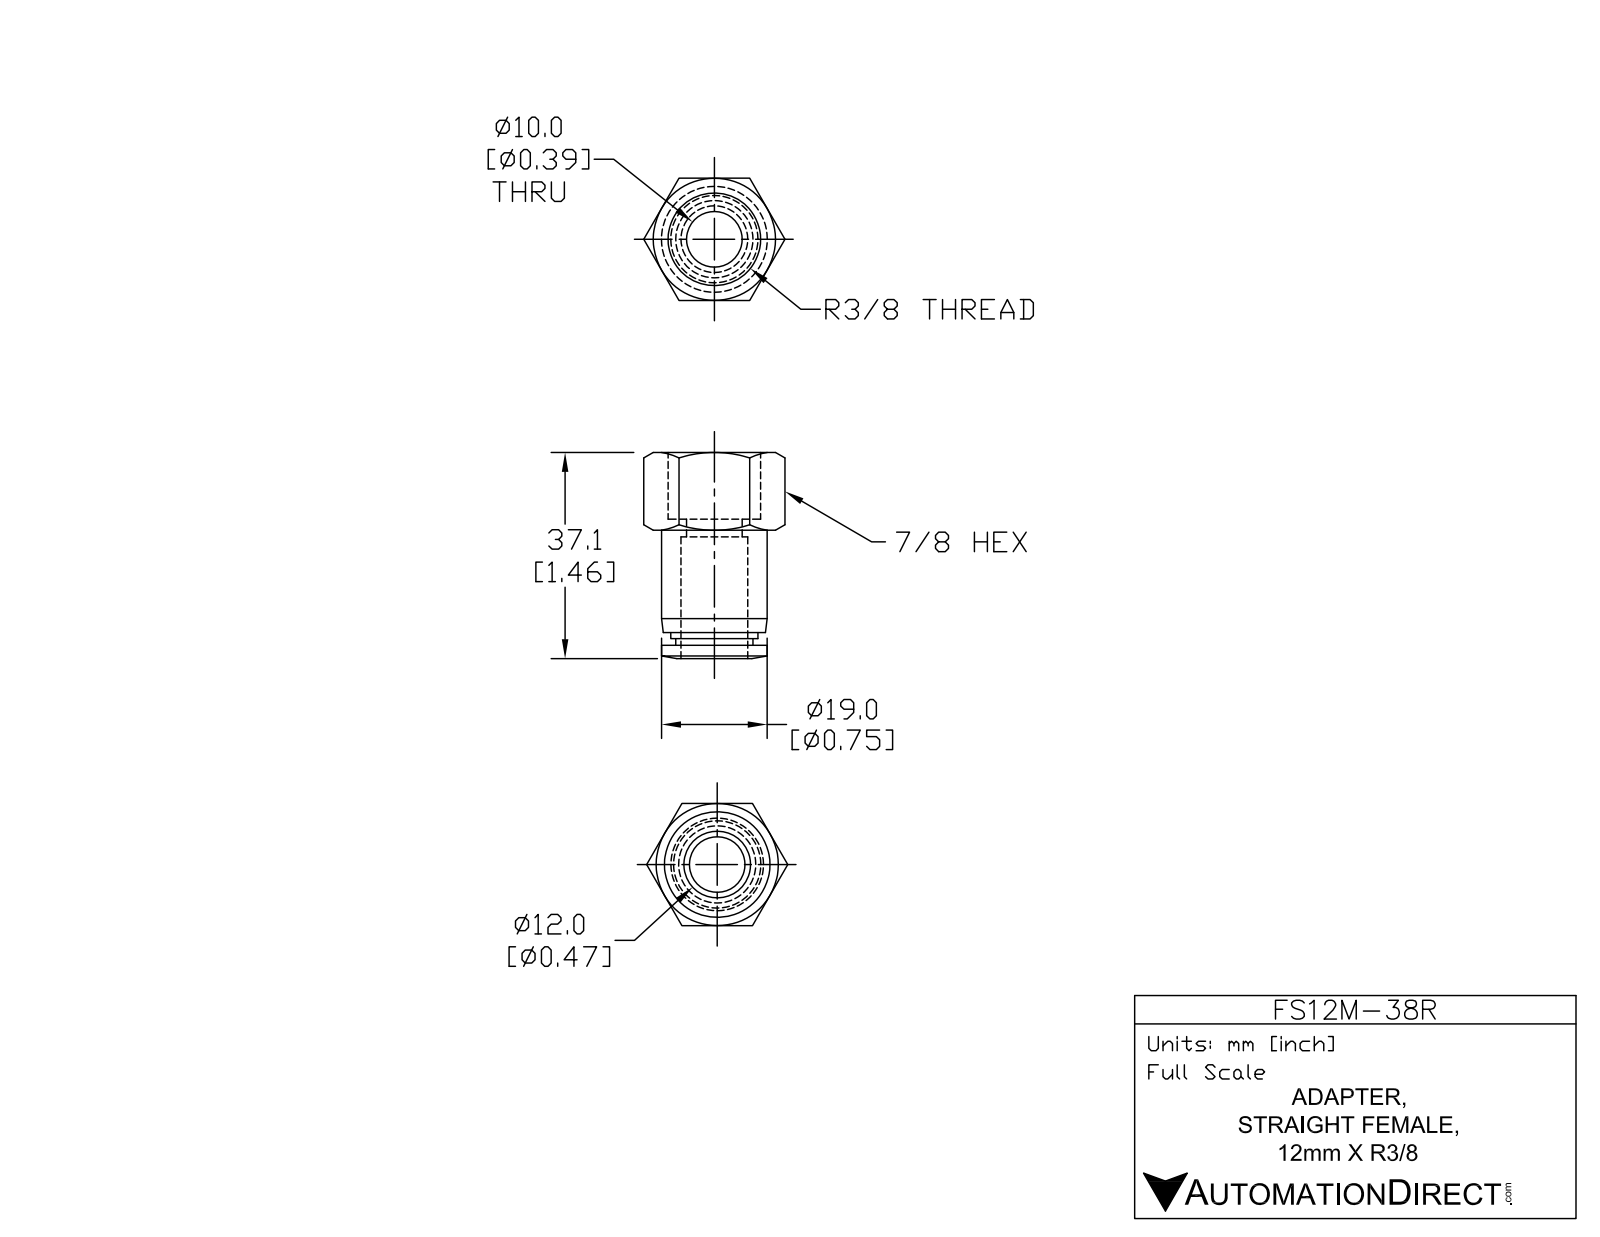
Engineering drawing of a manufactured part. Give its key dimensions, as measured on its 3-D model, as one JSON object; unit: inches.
{"part_name": "FS12M-38R", "step_written_by": "SolidWorks 2015 (AUTOMOTIVE_DESIGN)", "units": "inches", "bodies": {"solids": 1, "faces": 48, "planar": 14, "cylindrical": 12, "other": 22}, "overall_size": [1.461, 1, 0.866], "volume_in3": 0.41, "surface_area_in2": 7.458, "round_holes": [[0.394, 1], [0.484, 1]], "round_bosses_or_shafts": [[0.748, 1], [0.618, 1], [0.547, 1]], "face_to_face_distances": [0.866, 1.366, 0.472, 0.894, 0.551, 0.079, 0.815, 0.047, 0.768, 1.276]}
